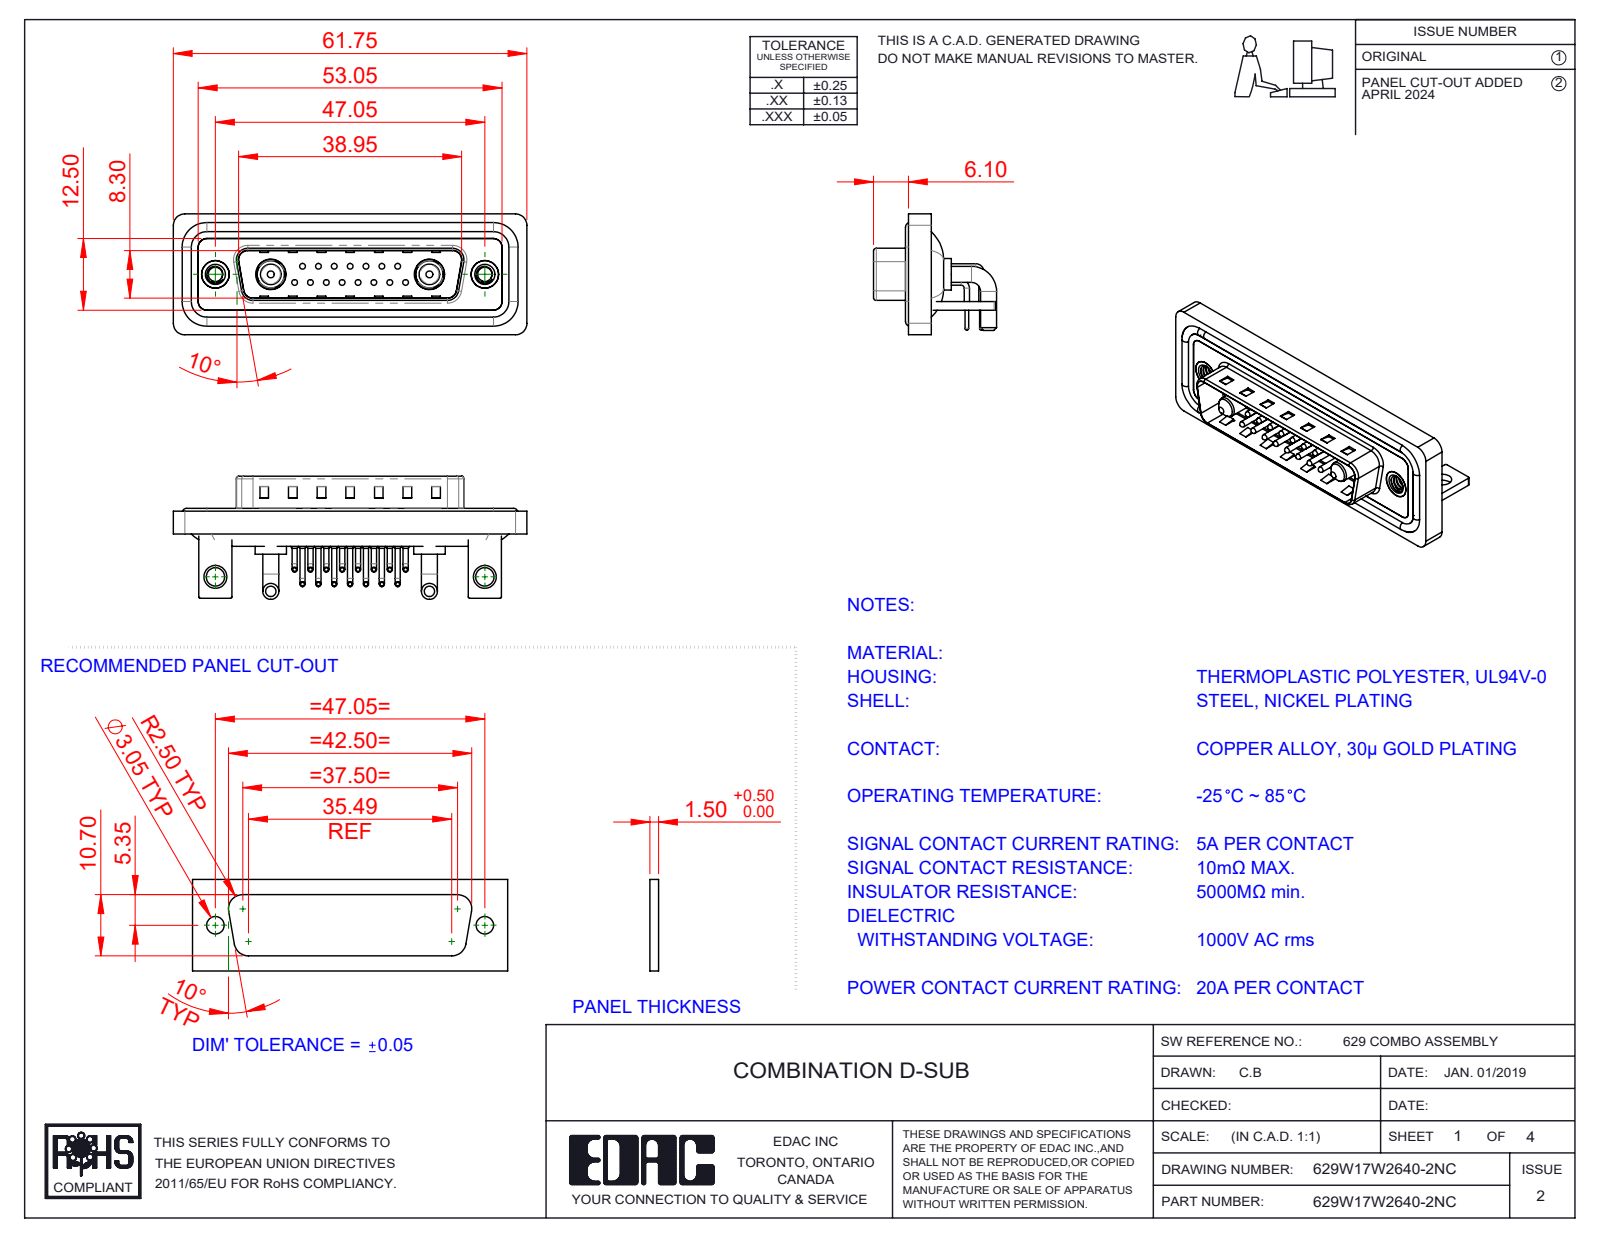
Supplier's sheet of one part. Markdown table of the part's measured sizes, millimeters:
| quantity | value |
| --- | --- |
| part name | 629W17W2640-2NC; Power Pin_20A RA; 629Combo Shell Front_25 Contacts; 629Combo Shell Rear_25 Contacts (+6 more) |
| STEP written by | SolidWorks 2023 (CONFIG_CONTROL_DESIGN) |
| units | millimeters |
| bodies | 28 solids, 2257 faces (1209 planar, 788 cylindrical, 260 other) |
| overall size | 61.75 × 21.5 × 21.1 |
| volume | 7 784 mm³ |
| surface area | 13 189 mm² |
| round holes (diameter × count) | 0.75 × 15, 1.6 × 15, 2 × 15, 2.5 × 2, 3.2 × 2, 4 × 2, 4.8 × 2, 4.85 × 2, 5 × 2, 5.3 × 2 |
| round bosses / shafts (diameter × count) | 0.9 × 30, 1.5 × 15, 1 × 15, 0.65 × 15, 2.8 × 4, 1.6 × 4, 5.5 × 2, 5.2 × 2 |
| partial cylindrical surfaces (radius × count) | 2 × 19, 1.5 × 18, 0.25 × 16, 1.01 × 15, 0.5 × 9, 1.6 × 8, 0.6 × 4, 0.65 × 4 |
| main face-to-face distances | 0.4, 0.8, 1.5, 2.1, 2.9, 1.1, 4.1, 1.6, 4.5, 3.7 |
| hole center spacings | 3.16, 2.77, 5.54, 8.31, 5.04, 7.49, 11.08, 5.03 |
